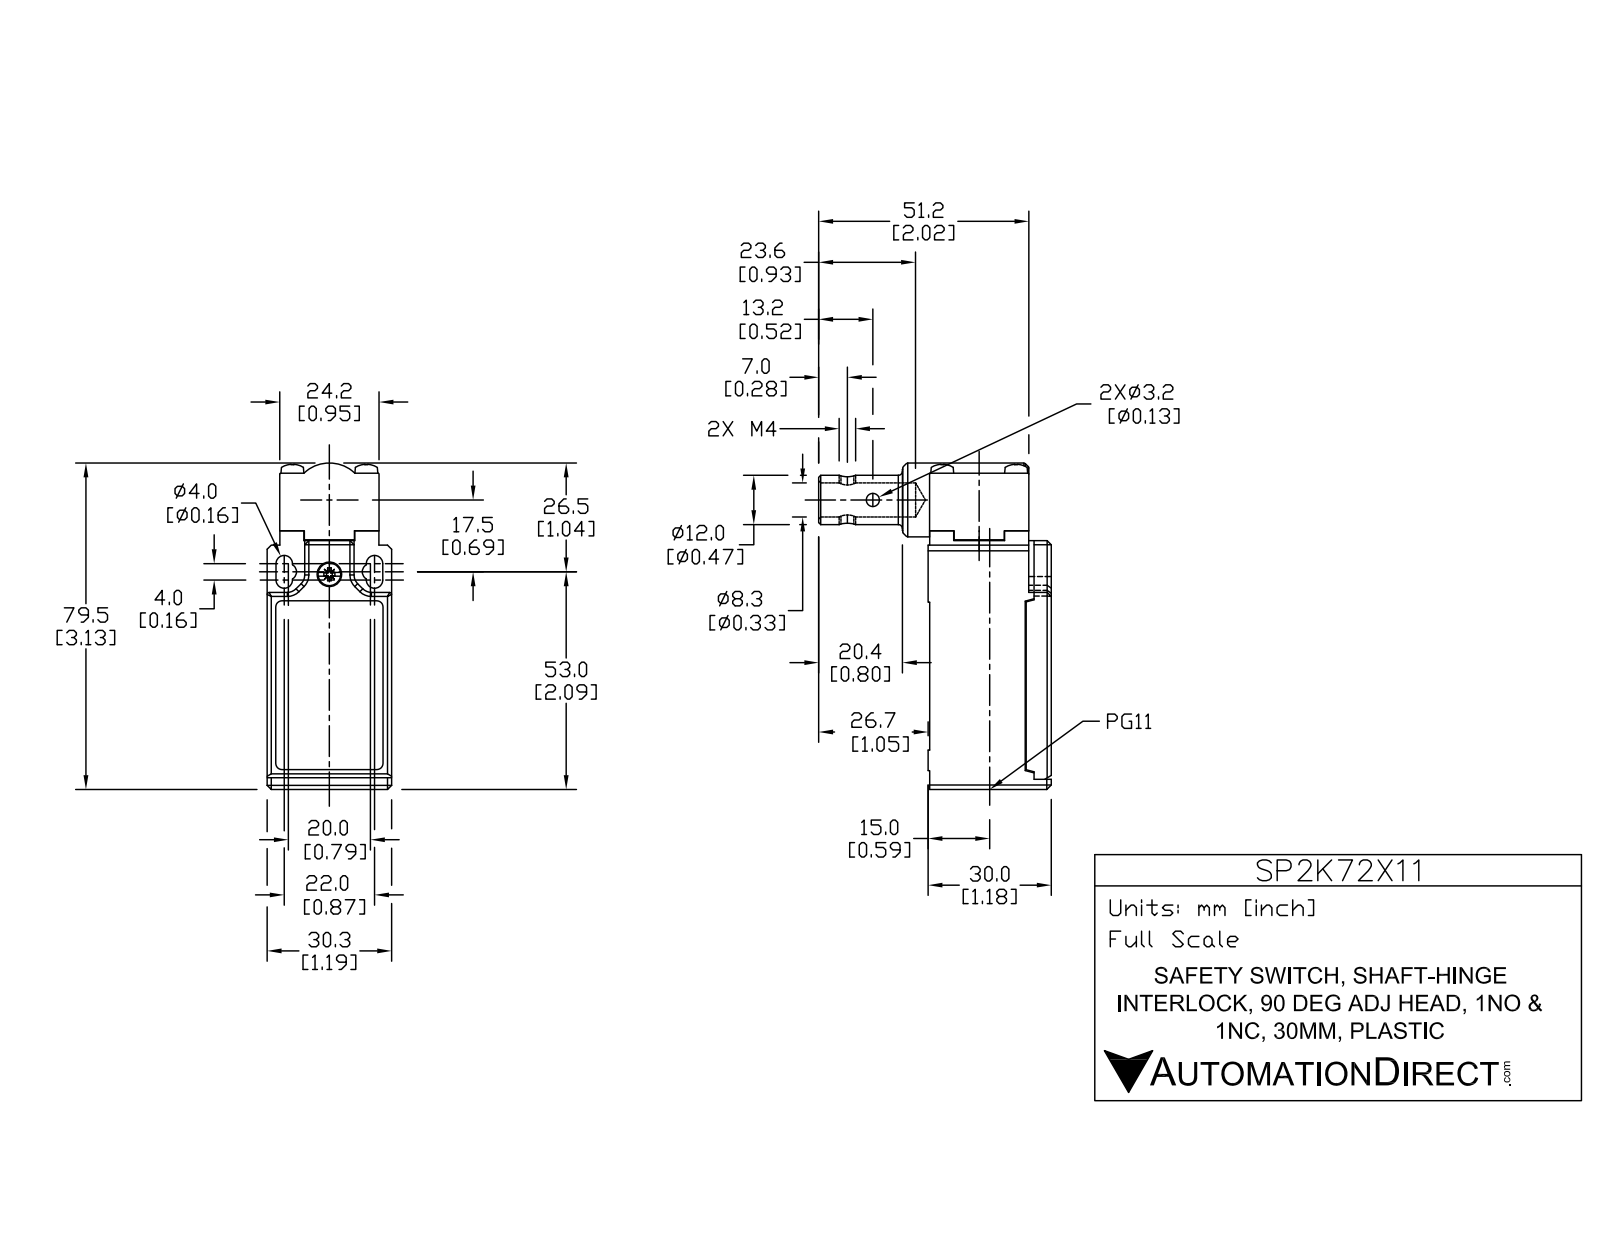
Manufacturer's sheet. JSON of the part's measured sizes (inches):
{"part_name": "SP2K72X11", "step_written_by": "SolidWorks 2017 (AUTOMOTIVE_DESIGN)", "units": "inches", "bodies": {"solids": 3, "faces": 200, "planar": 106, "cylindrical": 64, "other": 30}, "overall_size": [3.15, 2.255, 1.193], "volume_in3": 3.858, "surface_area_in2": 24.71, "round_holes": [[0.126, 1], [0.157, 1], [0.236, 1], [0.327, 1], [0.465, 1], [0.587, 1], [0.669, 1], [0.748, 1]], "round_bosses_or_shafts": [[0.22, 5], [0.709, 1], [0.472, 1]], "partial_cylinders_radius": [[0.079, 6], [0.02, 4], [0.118, 4], [0.394, 1], [0.4, 1]], "face_to_face_distances": [1.193, 1.165, 0.945, 0.124, 1.069, 0.22, 2.406, 1.181, 0.961, 0.016], "hole_center_spacings": [0.713, 1.102]}
